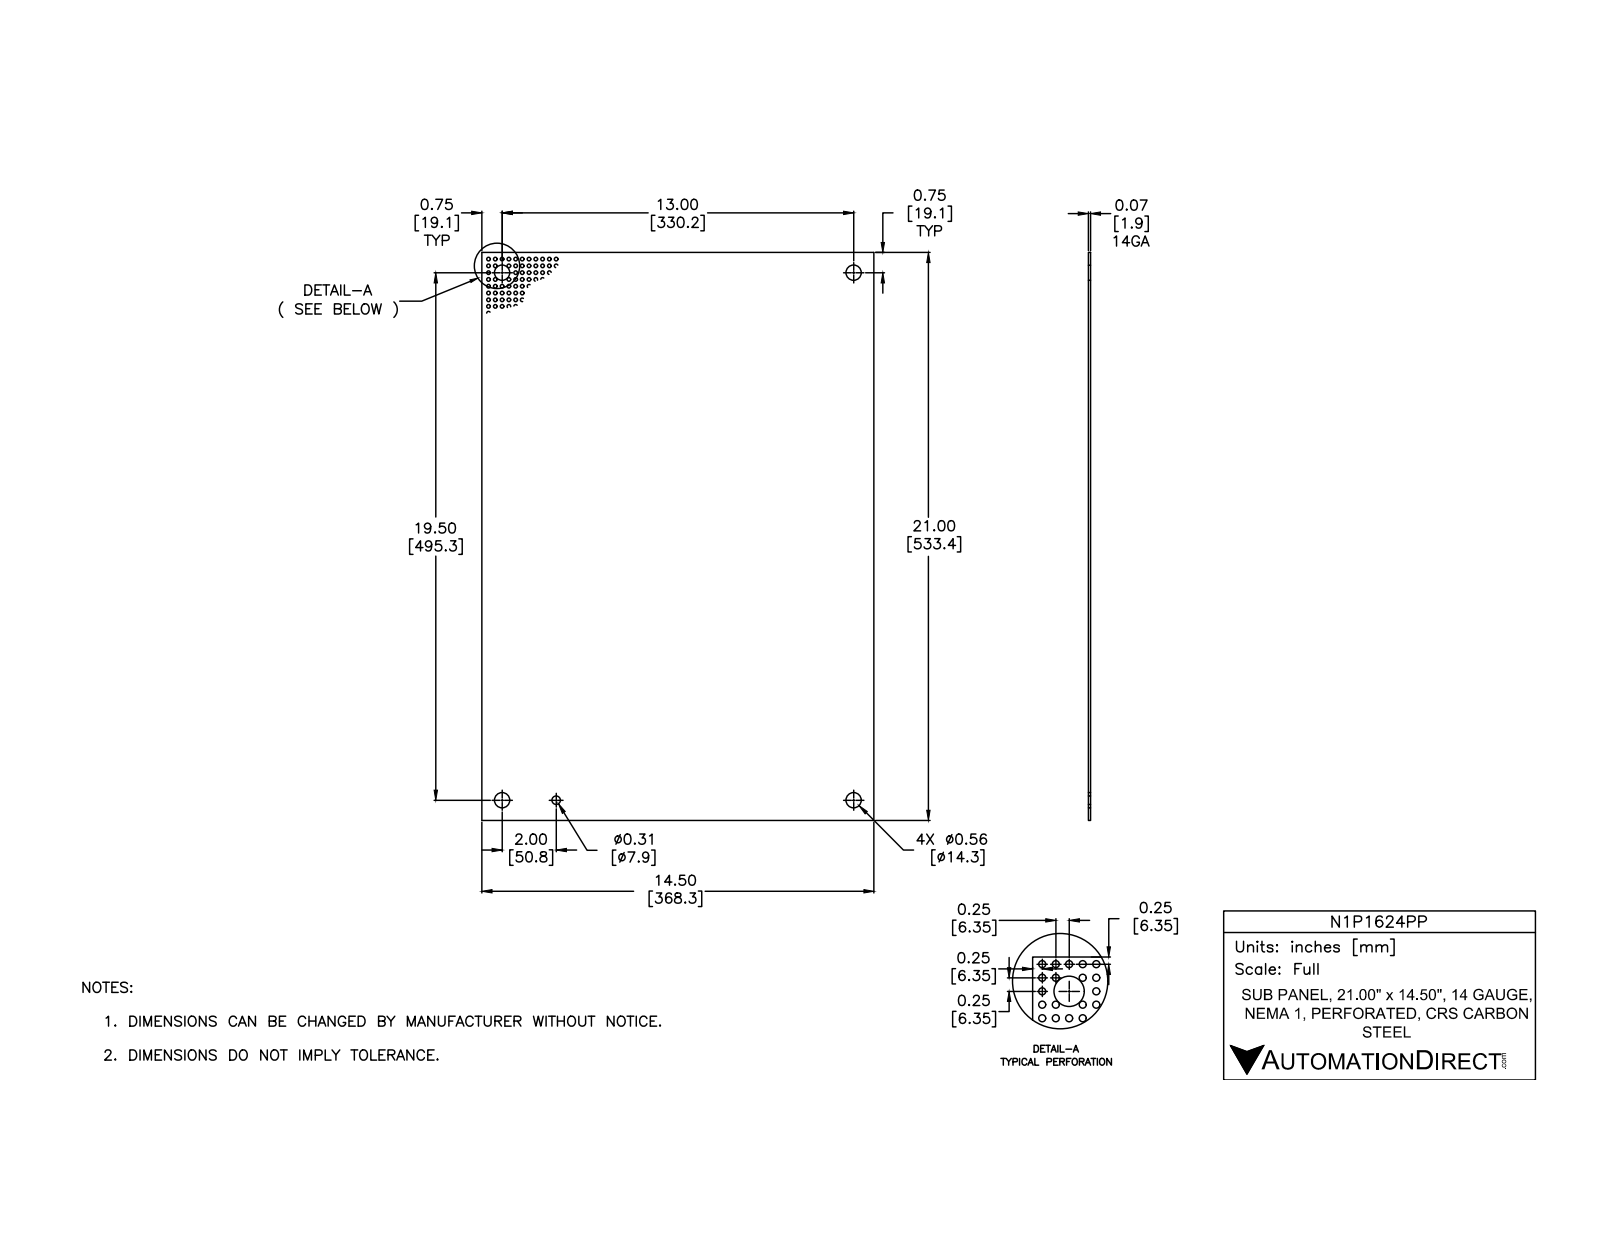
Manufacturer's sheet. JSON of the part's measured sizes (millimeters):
{"part_name": "N1P_PP-LARGE", "step_written_by": "Autodesk Inventor 2012 (AUTOMOTIVE_DESIGN)", "units": "millimeters", "bodies": {"solids": 1, "faces": 11, "planar": 6, "cylindrical": 5, "other": 0}, "overall_size": [533.4, 368.3, 1.9], "volume_mm3": 367900, "surface_area_mm2": 395300, "round_holes": [[14.3, 4], [7.9, 1]], "face_to_face_distances": [1.9, 368.3, 533.4], "hole_center_spacings": [330.2, 495.3, 595.3, 50.8, 279.4, 497.9, 568.7]}
